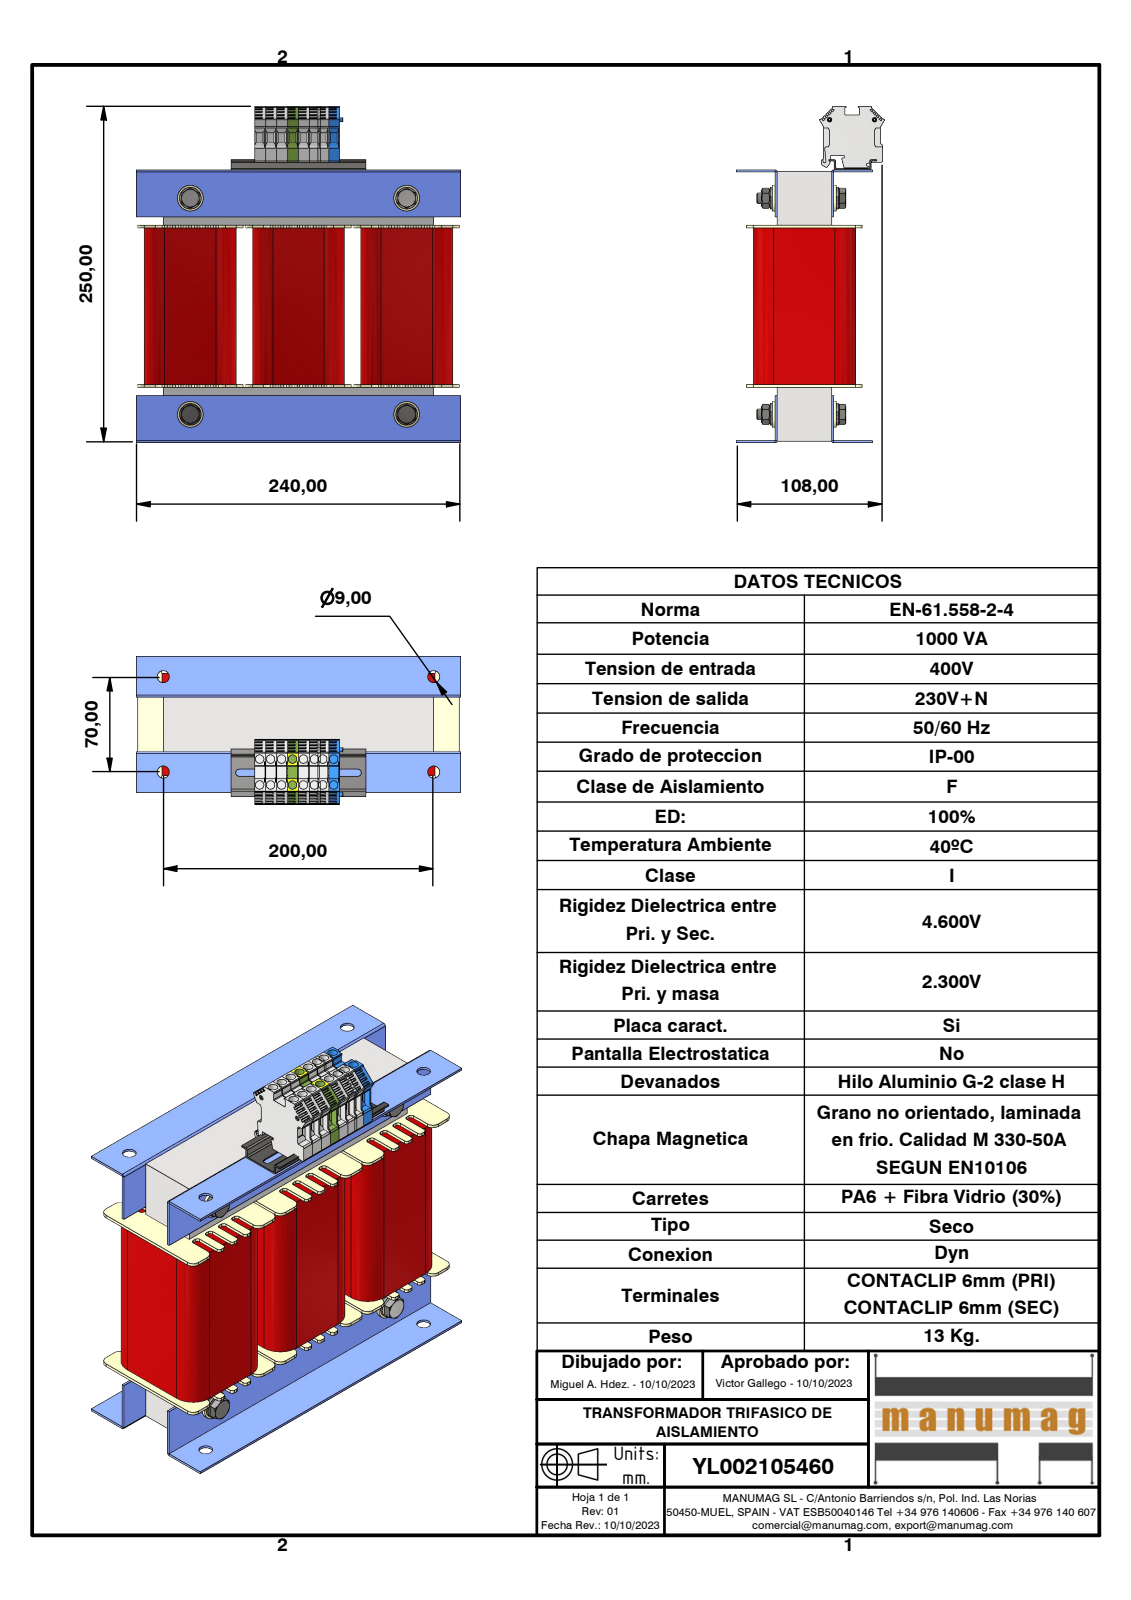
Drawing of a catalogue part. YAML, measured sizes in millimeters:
part_name: "YL002105460; 3UI120 200 x 200 - 40 (Rc40); UI 120_40; RC40 NT040 (+8 more)"
step_written_by: "Autodesk Inventor 2023 (AUTOMOTIVE_DESIGN)"
units: millimeters
bodies: {solids: 41, faces: 2898, planar: 2018, cylindrical: 712, other: 168}
overall_size: [249.05, 240, 109]
volume: 2615000
surface_area: 518690
round_holes:
  - {diameter: 6.3, count: 16}
  - {diameter: 6.65, count: 4}
  - {diameter: 8, count: 4}
  - {diameter: 8.4, count: 4}
  - {diameter: 9, count: 4}
  - {diameter: 10.5, count: 4}
  - {diameter: 11, count: 4}
  - {diameter: 2.4, count: 2}
  - {diameter: 2.5, count: 2}
  - {diameter: 2.75, count: 2}
  - {diameter: 2.95, count: 2}
round_bosses_or_shafts:
  - {diameter: 19, count: 4}
  - {diameter: 16, count: 4}
  - {diameter: 11.4, count: 4}
  - {diameter: 9.6, count: 4}
  - {diameter: 7.32, count: 4}
partial_cylinders:
  - {radius: 2, count: 85}
  - {radius: 5, count: 24}
  - {radius: 0.25, count: 16}
  - {radius: 1, count: 15}
  - {radius: 15, count: 12}
  - {radius: 2.6, count: 8}
  - {radius: 0.3, count: 5}
  - {radius: 0.5, count: 5}
face_to_face_distances: [40, 1.5, 80, 160, 41.5, 120, 14, 54, 43, 161]
hole_center_spacings: [8.1, 20.65, 16.2, 19, 24.97, 24.3, 30.85, 14.25]
